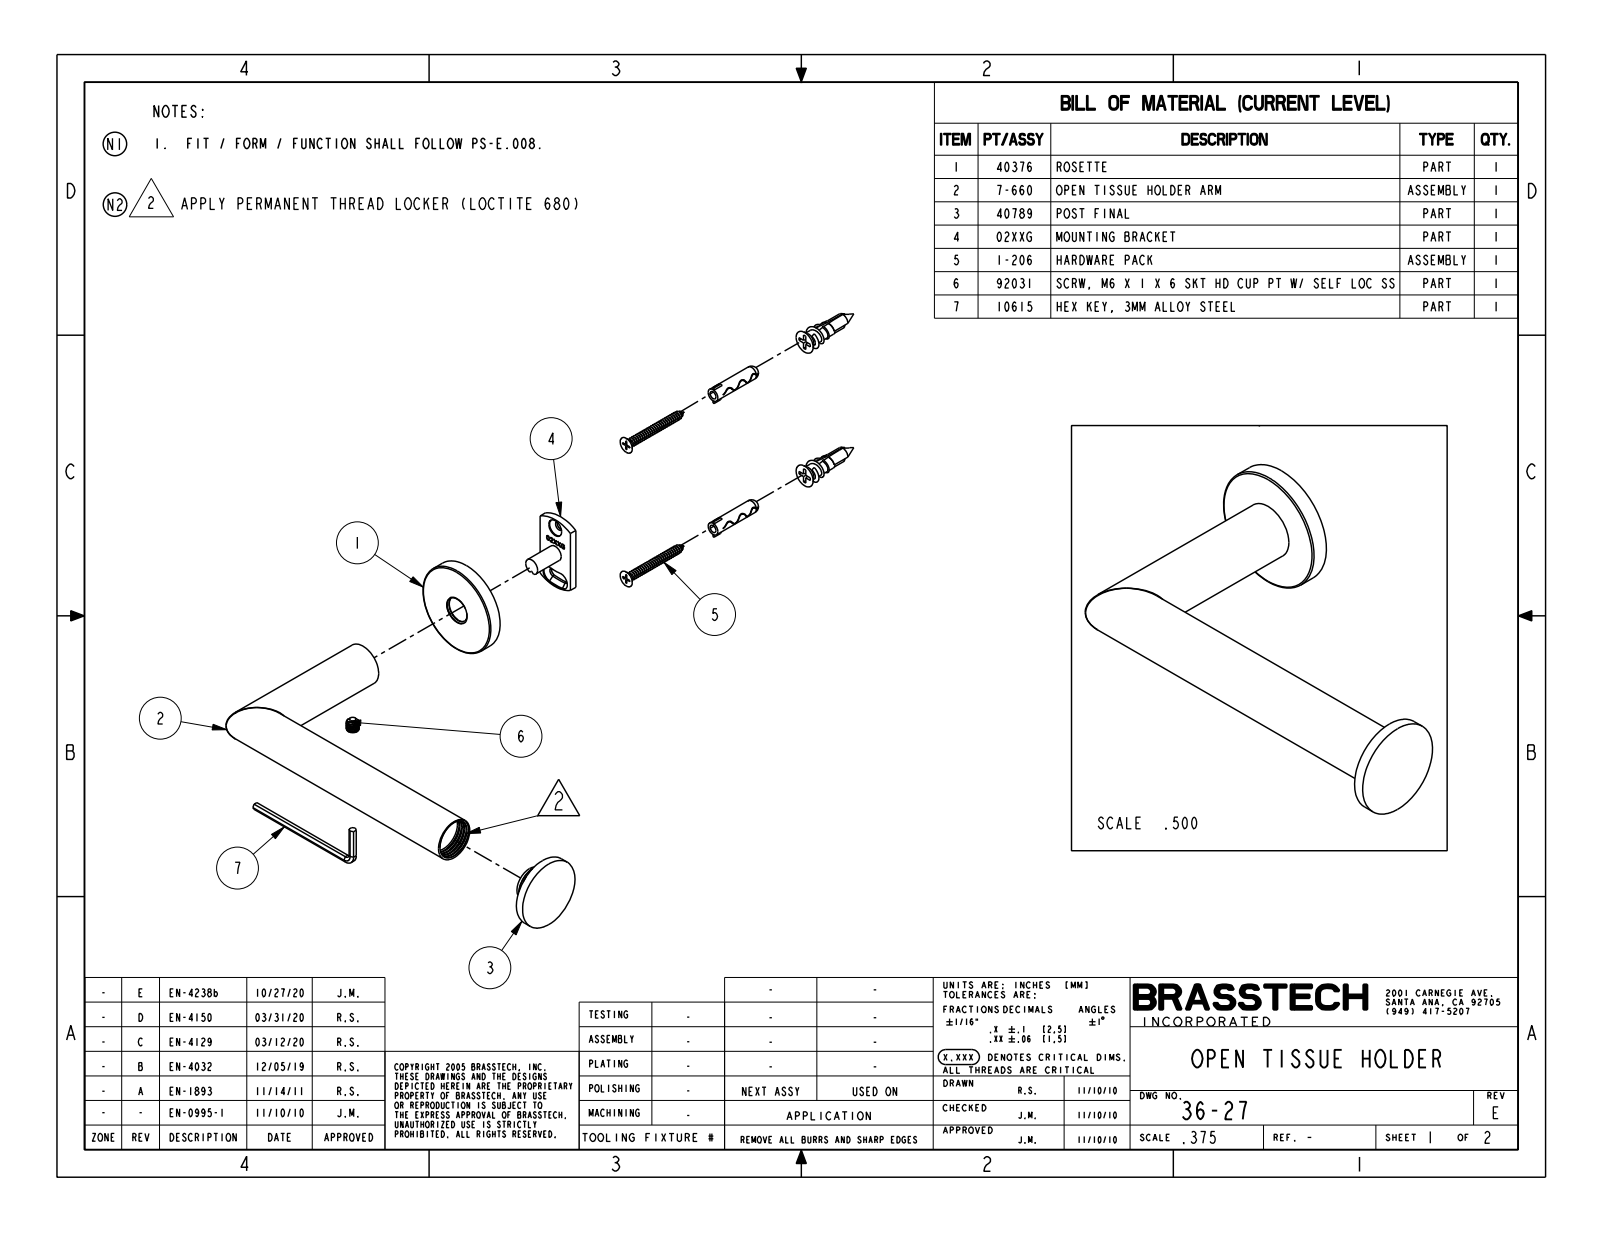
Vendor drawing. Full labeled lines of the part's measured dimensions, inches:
Part name (STEP PRODUCT): 36-27
STEP written by: CREO PARAMETRIC BY PTC INC, 2018400 (AUTOMOTIVE_DESIGN)
Units: inches
Bodies: 1 solid, 18 faces (4 planar, 8 cylindrical, 6 other)
Overall size (bounding box): 6.15 × 3.695 × 1.75
Volume: 4.911 in³ · Surface area: 28.76 in²
Round bosses / shafts (diameter × count): ⌀0.81 ×2, ⌀1.75 ×1, ⌀1.358 ×1
Main face-to-face distances: 0.26, 0.157
